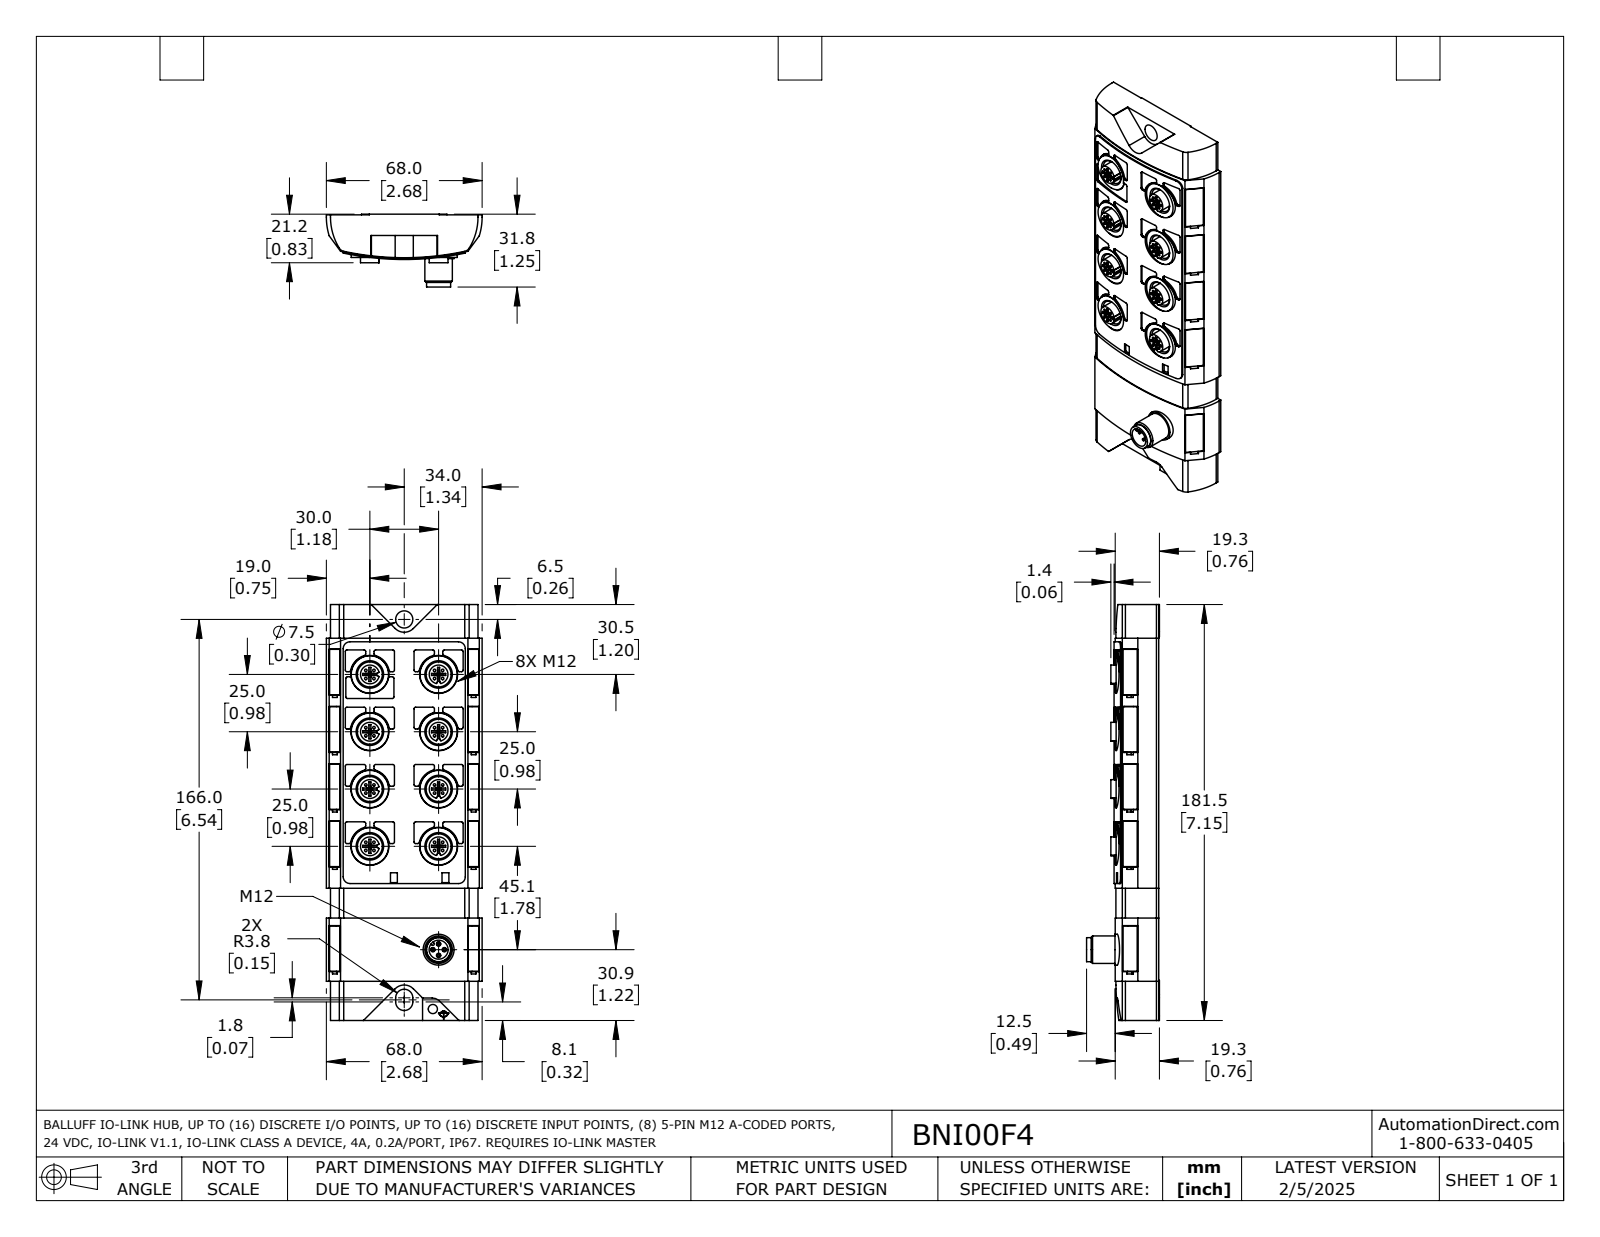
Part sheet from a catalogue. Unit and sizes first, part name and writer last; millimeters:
Units: millimetres
Overall size (bounding box): 181.5 × 68 × 31.8
Round holes (diameter × count): ⌀1.1 ×40, ⌀10.9 ×8, ⌀16.6 ×8, ⌀1.9 ×4, ⌀4 ×1, ⌀7.5 ×1, ⌀8.3 ×1
Round bosses / shafts (diameter × count): ⌀16.3 ×8, ⌀8.2 ×8, ⌀1 ×4, ⌀13.5 ×1, ⌀12 ×1, ⌀10.5 ×1
Partial cylindrical surfaces — rounded edges, fillets, slot ends (radius × count): R0.7 ×86, R0.8 ×40, R0.2 ×16, R8.6 ×8, R0.3 ×5, R3 ×3, R3 ×3, R1.8 ×2
Main face-to-face distances: 8, 18.6, 181.5, 18.9, 12.4, 7.9, 8.1, 9, 12.1, 6.5
Hole centre spacings: 2.5, 3.5, 25, 23.3, 26.8, 5, 25.2, 48.3
Volume: 199 100 mm³ · Surface area: 45 480 mm²
Bodies: 1 solid, 921 faces (488 planar, 407 cylindrical, 26 other)
Part name (STEP PRODUCT): BNI00F4
STEP written by: SolidWorks 2021 (AUTOMOTIVE_DESIGN)
